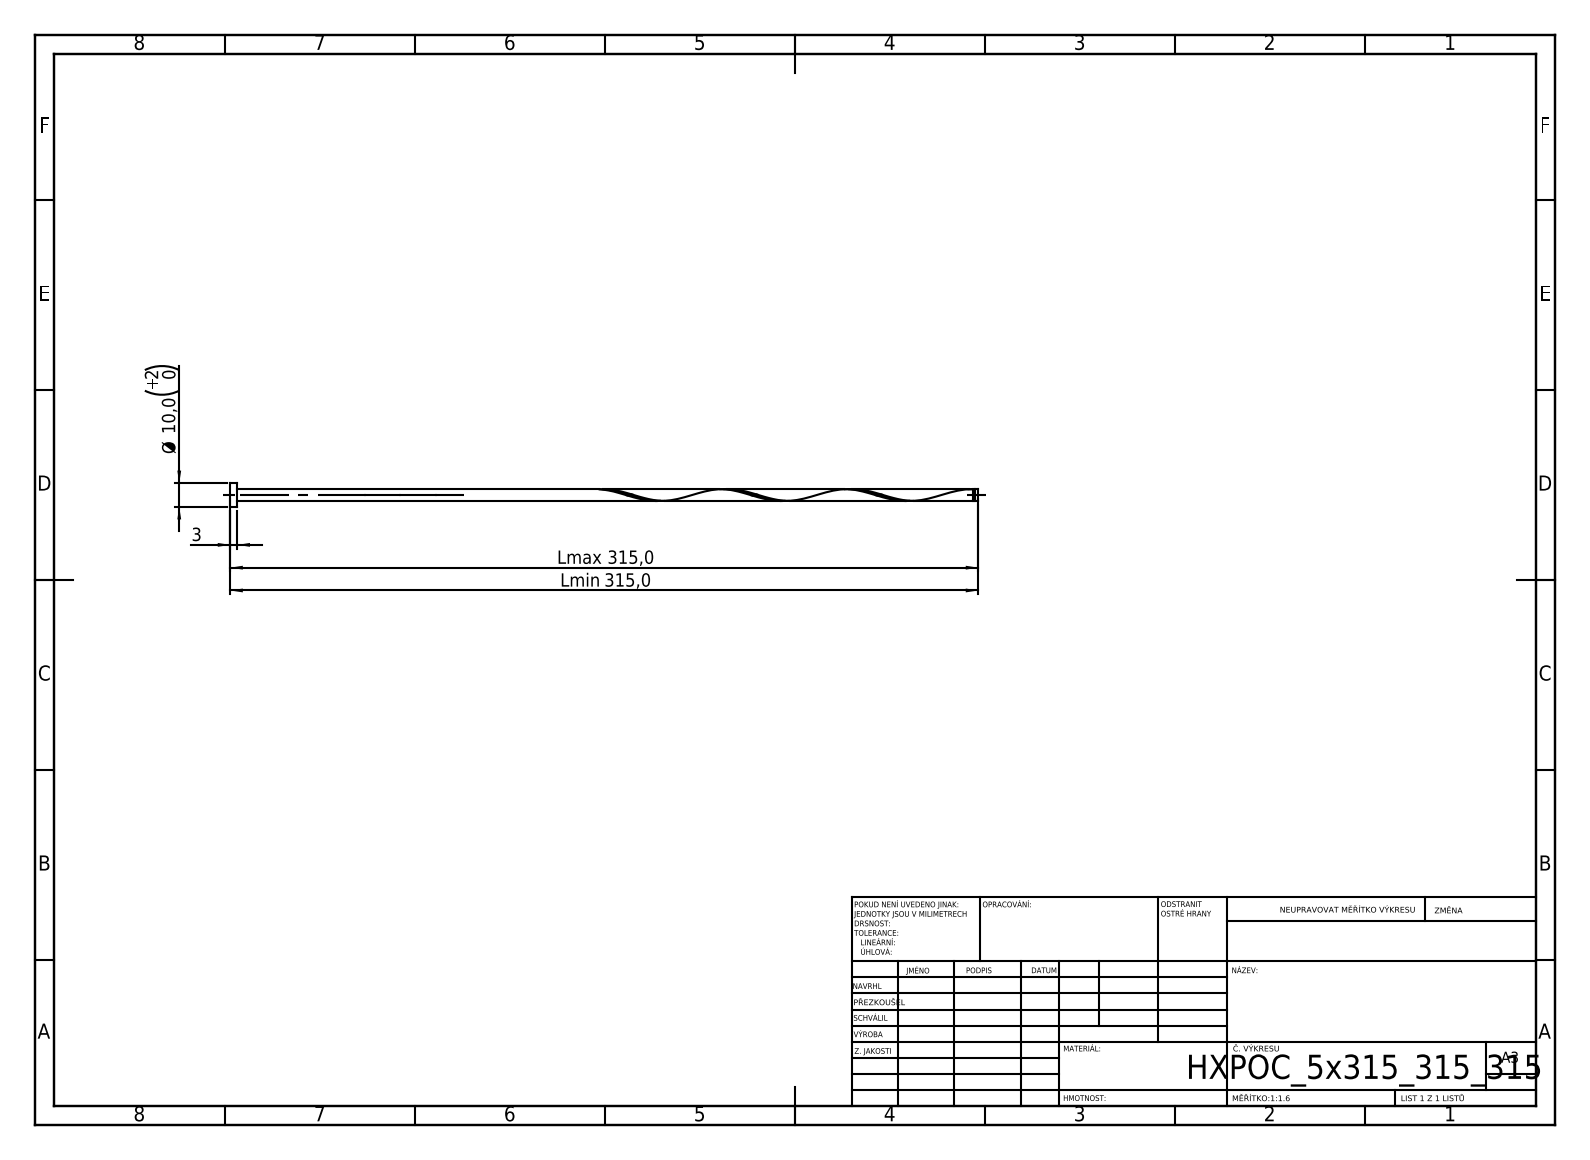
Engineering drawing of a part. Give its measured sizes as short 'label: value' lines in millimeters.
written by: SolidWorks 2019 (CONFIG_CONTROL_DESIGN)
unit: mm
bodies: 1 solid, 16 faces (6 planar, 9 cylindrical, 1 other)
size: 315 × 10 × 10
volume: 7 670 mm³; area: 6 891 mm²
bosses: 1× ⌀10, 1× ⌀5, 1× ⌀4
face distances: 3, 315, 312, 313.6, 310.6, 1.4, 312.6, 309.6, 1, 2.4
